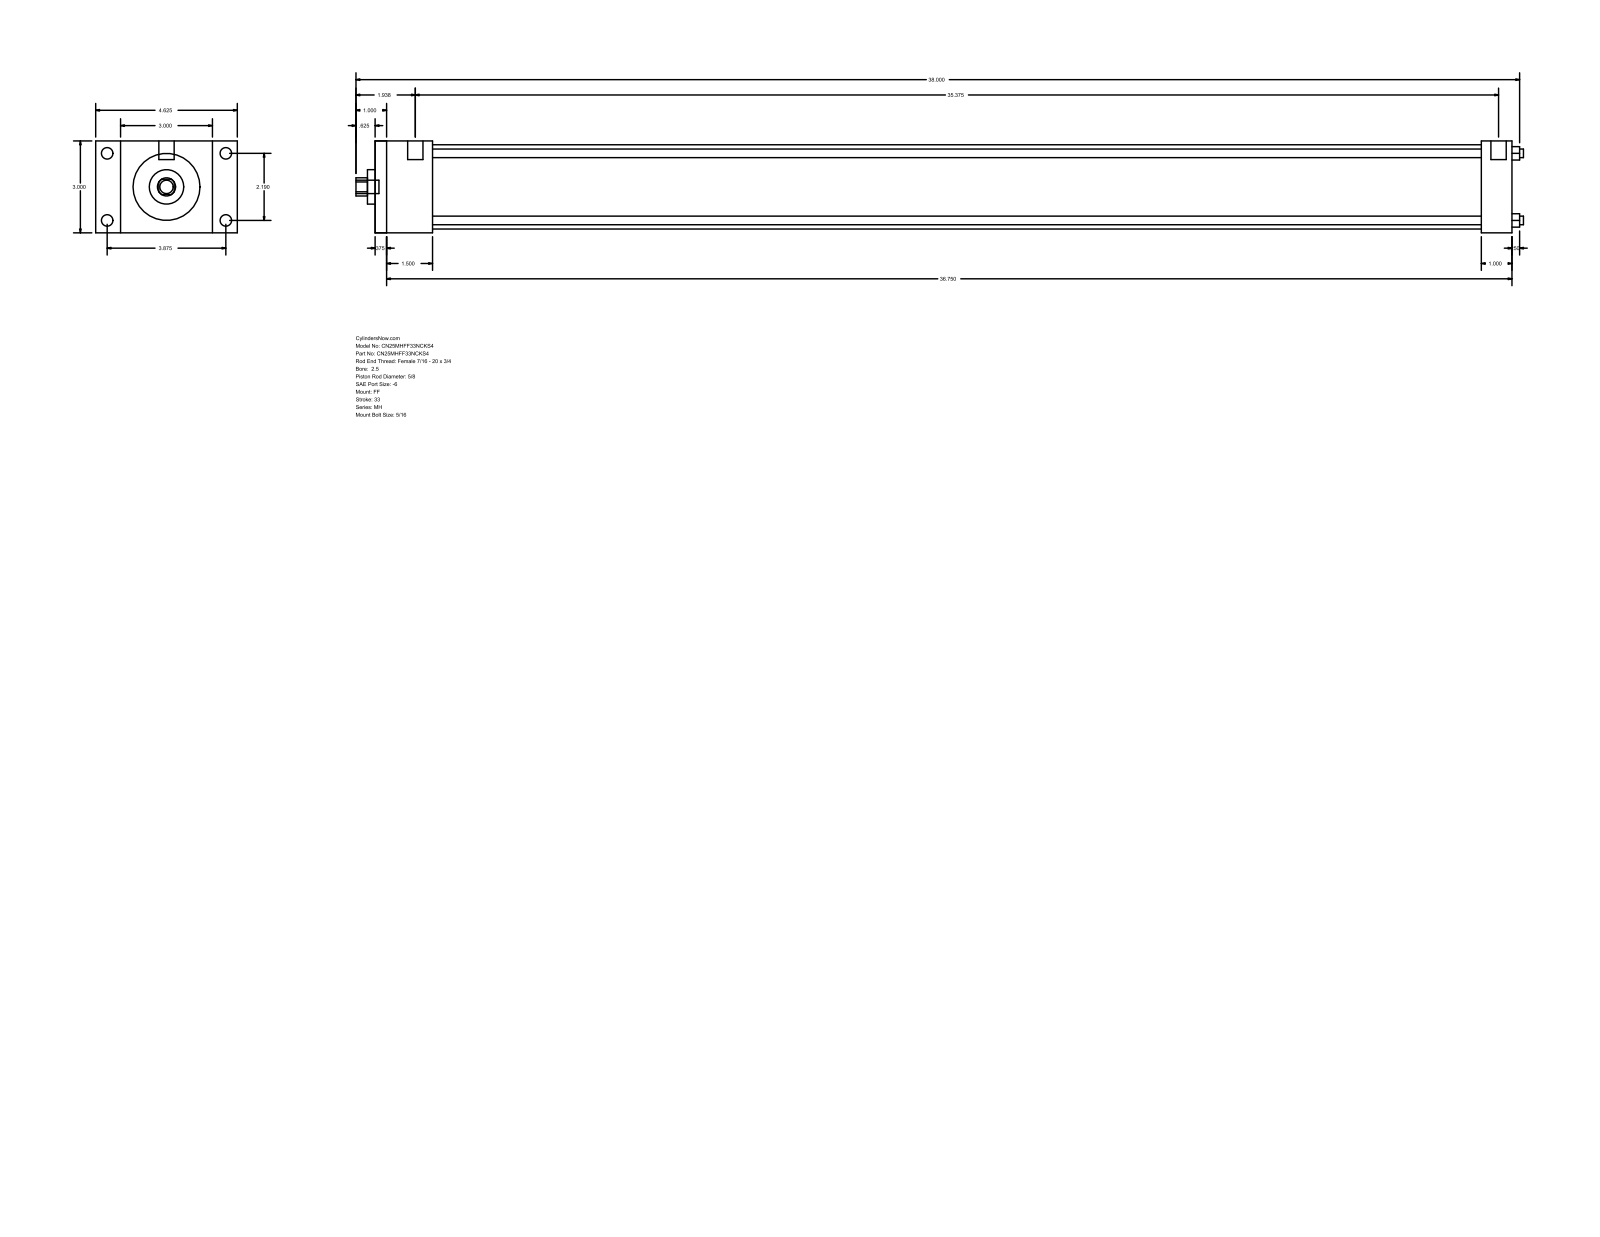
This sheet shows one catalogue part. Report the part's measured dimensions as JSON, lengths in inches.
{"part_name": "MH_FF__0250_0.625", "step_written_by": "GSSL Pune (CONFIG_CONTROL_DESIGN)", "units": "inches", "bodies": {"solids": 0, "faces": 92, "planar": 64, "cylindrical": 28, "other": 0}, "overall_size": [38.125, 4.625, 3], "round_holes": [[0.281, 4], [0.625, 1], [1.125, 1], [2.75, 1]], "round_bosses_or_shafts": [[0.375, 4], [0.219, 4], [0.5, 2], [0.437, 1]], "partial_cylinders_radius": [[0.297, 1]], "face_to_face_distances": [3, 37.125, 0.375, 36.75, 1, 1.875, 36.125, 1.5, 35.75, 34.25], "hole_center_spacings": [1.548, 2.19, 3.097]}
